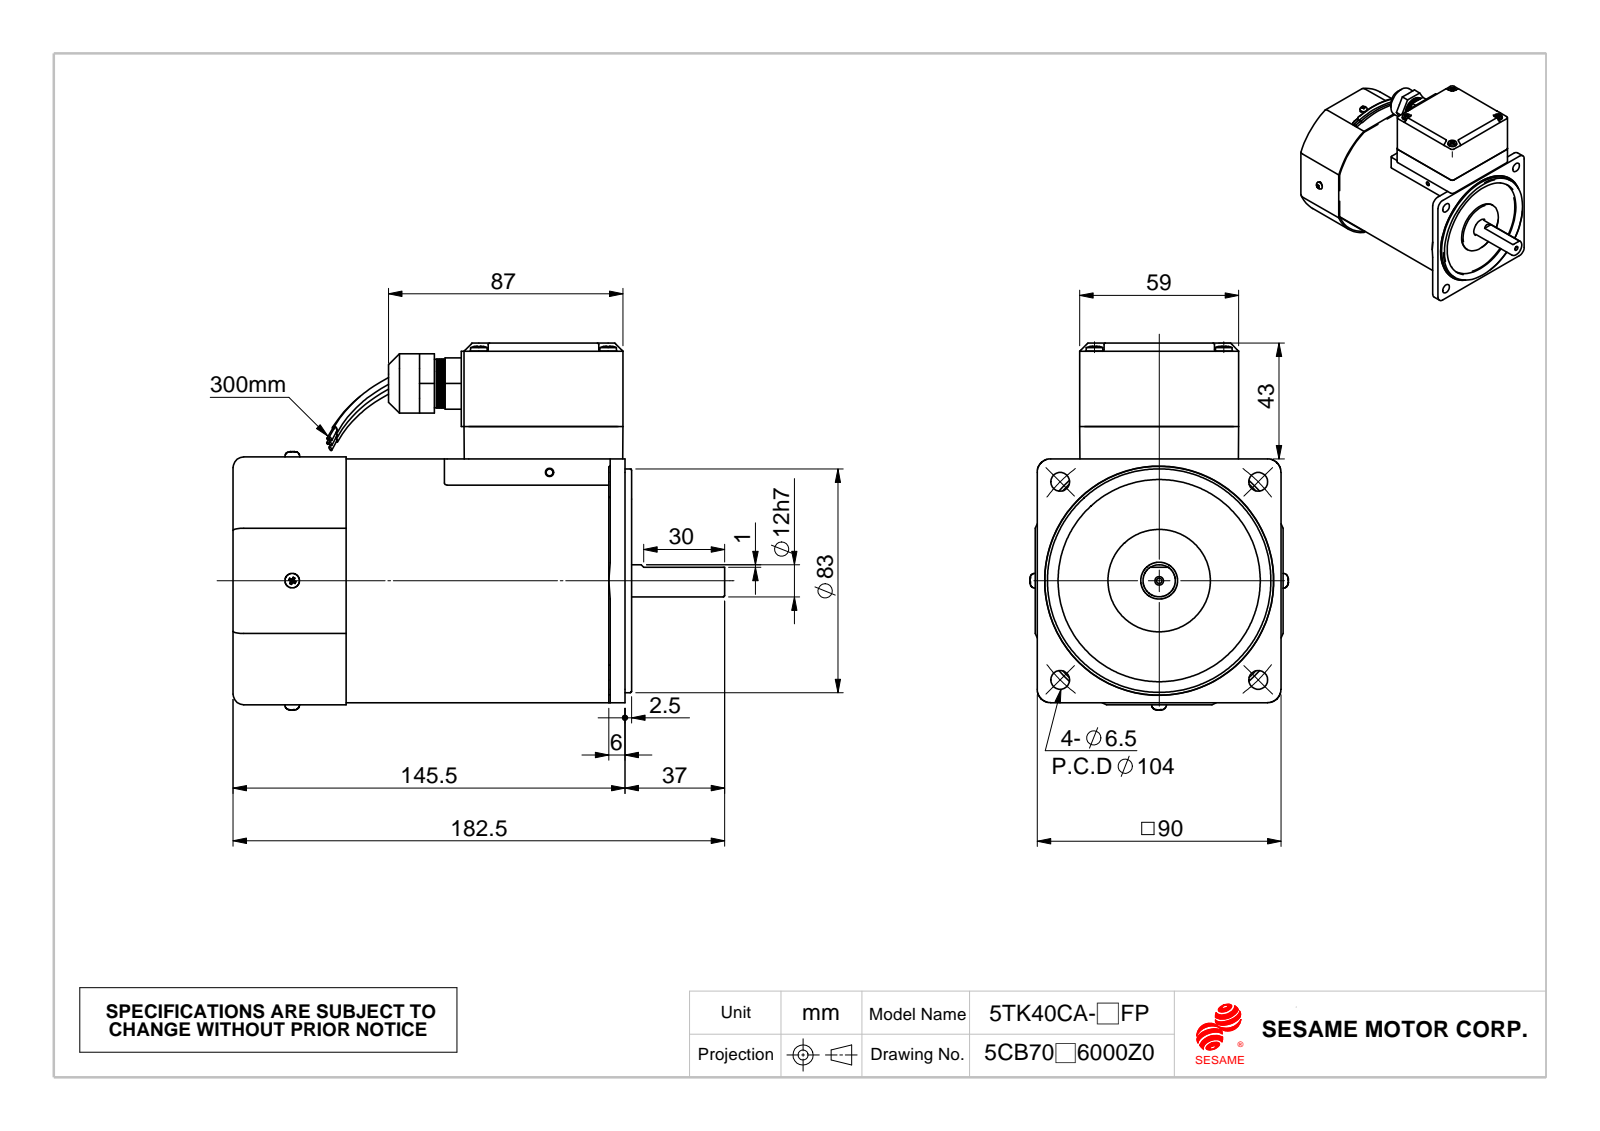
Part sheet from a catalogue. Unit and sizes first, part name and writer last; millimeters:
Units: millimetres
Overall size (bounding box): 182.5 × 136.21 × 95.92
Round holes (diameter × count): ⌀3.3 ×4, ⌀3.5 ×4, ⌀3.9 ×4, ⌀4.3 ×4, ⌀7 ×4, ⌀2.5 ×3, ⌀2 ×1, ⌀6.5 ×1, ⌀11 ×1, ⌀12 ×1, ⌀13.7 ×1, ⌀14.5 ×1
Round bosses / shafts (diameter × count): ⌀3 ×6, ⌀6.3 ×4, ⌀11 ×3, ⌀5.5 ×2, ⌀90.5 ×1, ⌀86 ×1, ⌀85 ×1, ⌀84 ×1
Partial cylindrical surfaces — rounded edges, fillets, slot ends (radius × count): R0.3 ×16, R2 ×16, R1 ×10, R4 ×10, R0.5 ×8, R3 ×8, R1.5 ×4, R1.75 ×4
Main face-to-face distances: 1, 12, 0.75, 91, 3.9, 16, 140, 143.9, 139, 142.9
Hole centre spacings: 48, 52, 73.54, 11.67, 12.35, 12.7, 24.93, 25
Volume: 1 035 000 mm³ · Surface area: 149 738 mm²
Bodies: 19 solids, 2721 faces (344 planar, 938 cylindrical, 1439 other)
Part name (STEP PRODUCT): Ts下墊片; M590Ts-F; 風扇蓋FC-9042-21; 90A_4.研磨 (+1 more)
STEP written by: SolidWorks 2010 (CONFIG_CONTROL_DESIGN)
